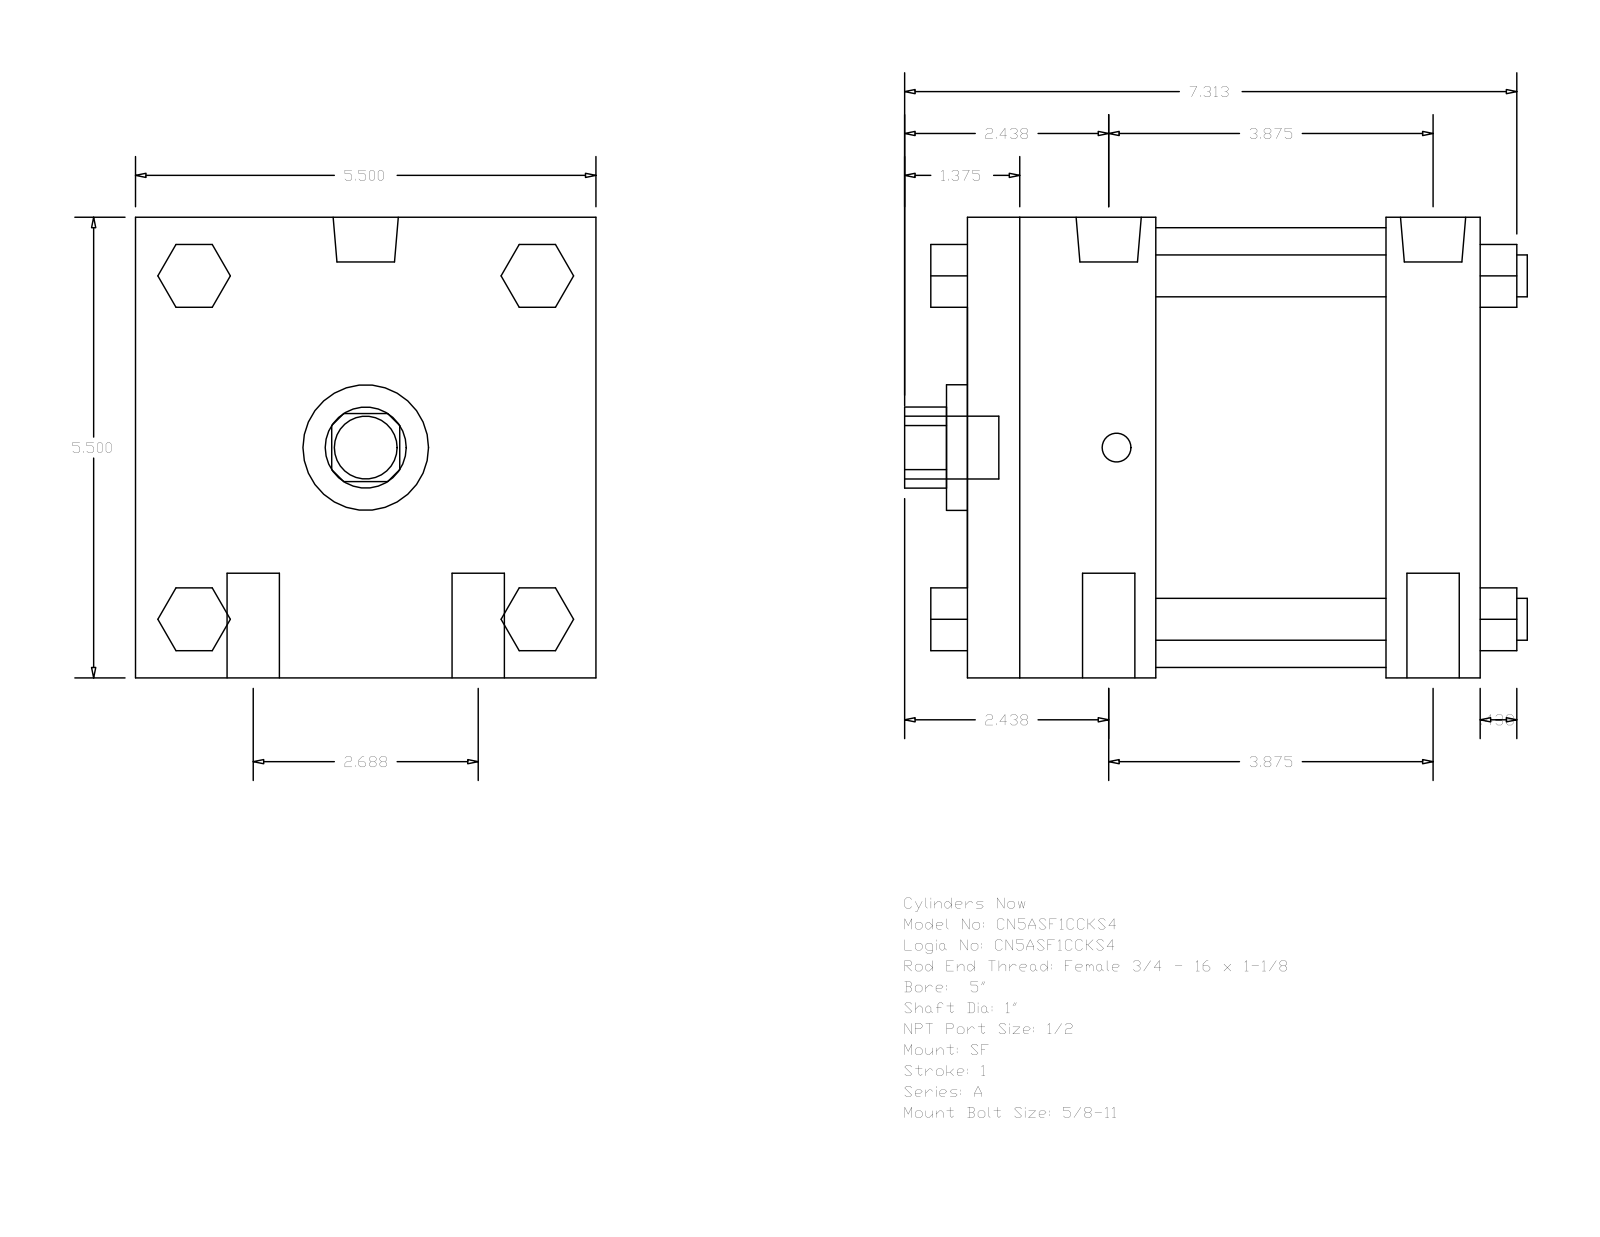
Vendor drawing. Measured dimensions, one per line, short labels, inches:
name: A_SF__0500_1
written by: GSSL Pune (CONFIG_CONTROL_DESIGN)
unit: in
bodies: 0 solids, 124 faces (94 planar, 30 cylindrical, 0 other)
size: 7.437 × 5.5 × 5.5
holes: 1× ⌀1, 1× ⌀1.5, 1× ⌀5.25
bosses: 4× ⌀0.625, 4× ⌀0.5, 2× ⌀0.778, 2× ⌀0.344, 1× ⌀0.75
rounds: 1× R0.484
face distances: 5.5, 6.125, 5, 1.125, 2.25, 2.75, 3.875, 0.75, 2.05, 3.55
